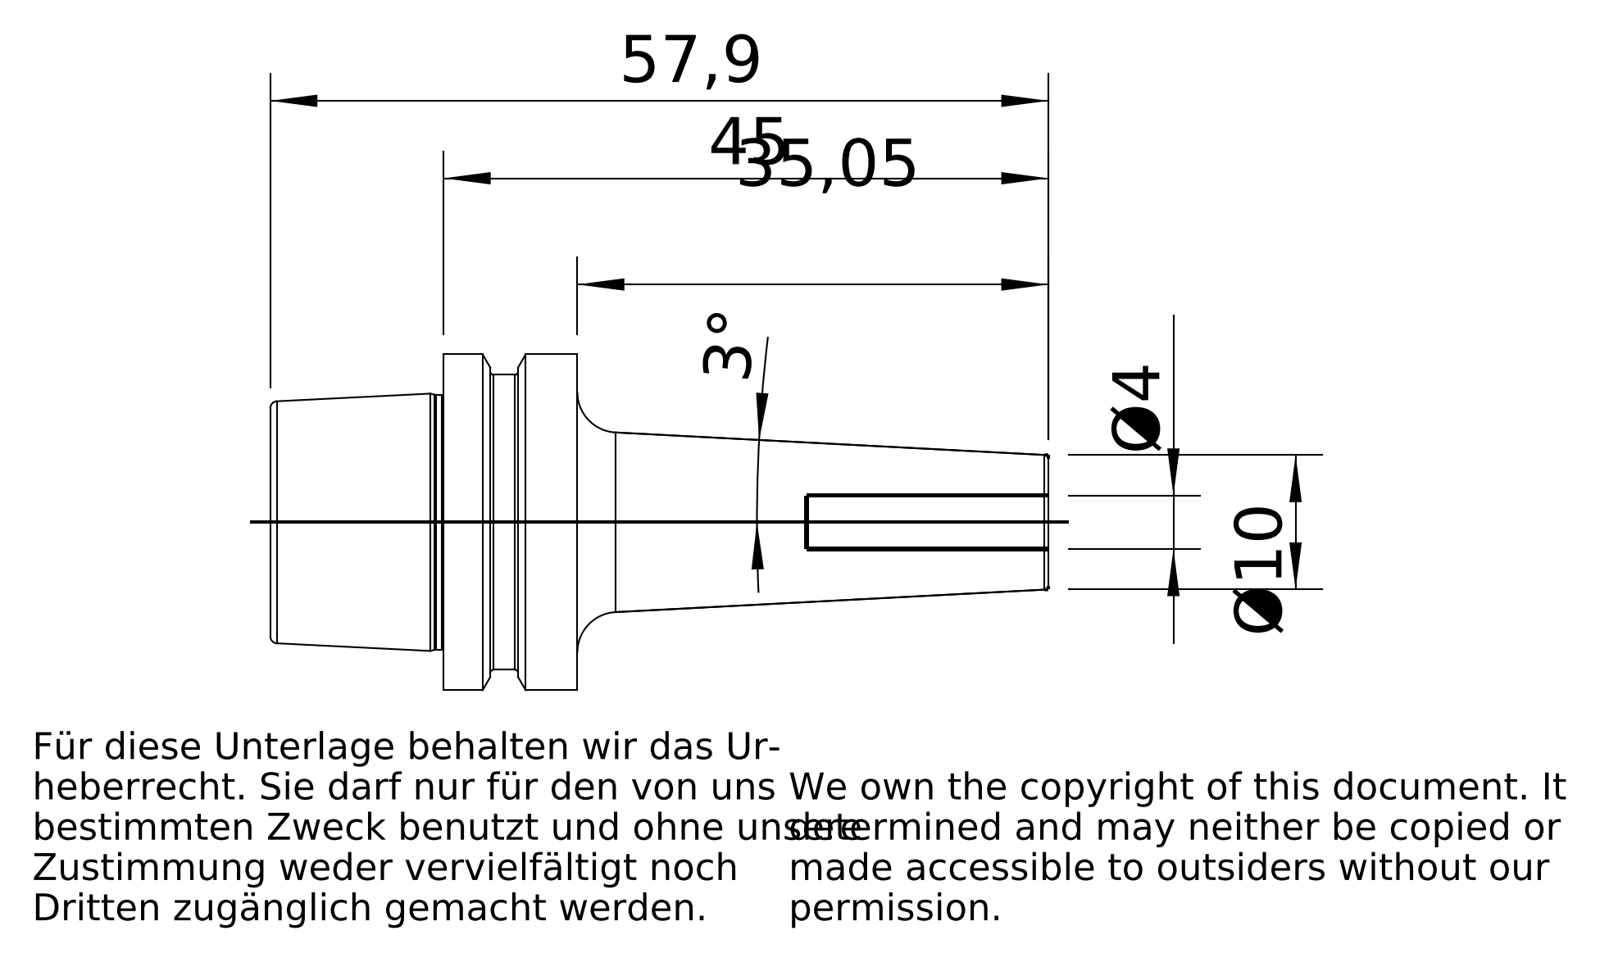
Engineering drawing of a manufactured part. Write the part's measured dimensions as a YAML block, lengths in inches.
part_name: "E25-180-04"
step_written_by: "PRO/ENGINEER BY PARAMETRIC TECHNOLOGY CORPORATION, 2010430 (CONFIG_CONTROL_DESIGN)"
units: inches
bodies: {solids: 1, faces: 60, planar: 8, cylindrical: 16, other: 36}
overall_size: [2.28, 0.984, 0.984]
volume: 0.521
surface_area: 7.66
round_holes:
  - {diameter: 0.157, count: 1}
  - {diameter: 0.553, count: 1}
  - {diameter: 0.648, count: 1}
round_bosses_or_shafts:
  - {diameter: 0.984, count: 1}
  - {diameter: 0.864, count: 1}
  - {diameter: 0.746, count: 1}
face_to_face_distances: [0.157, 0.234, 0.392, 1.772, 1.537, 1.38, 0.508, 0.742, 0.9, 2.28]
